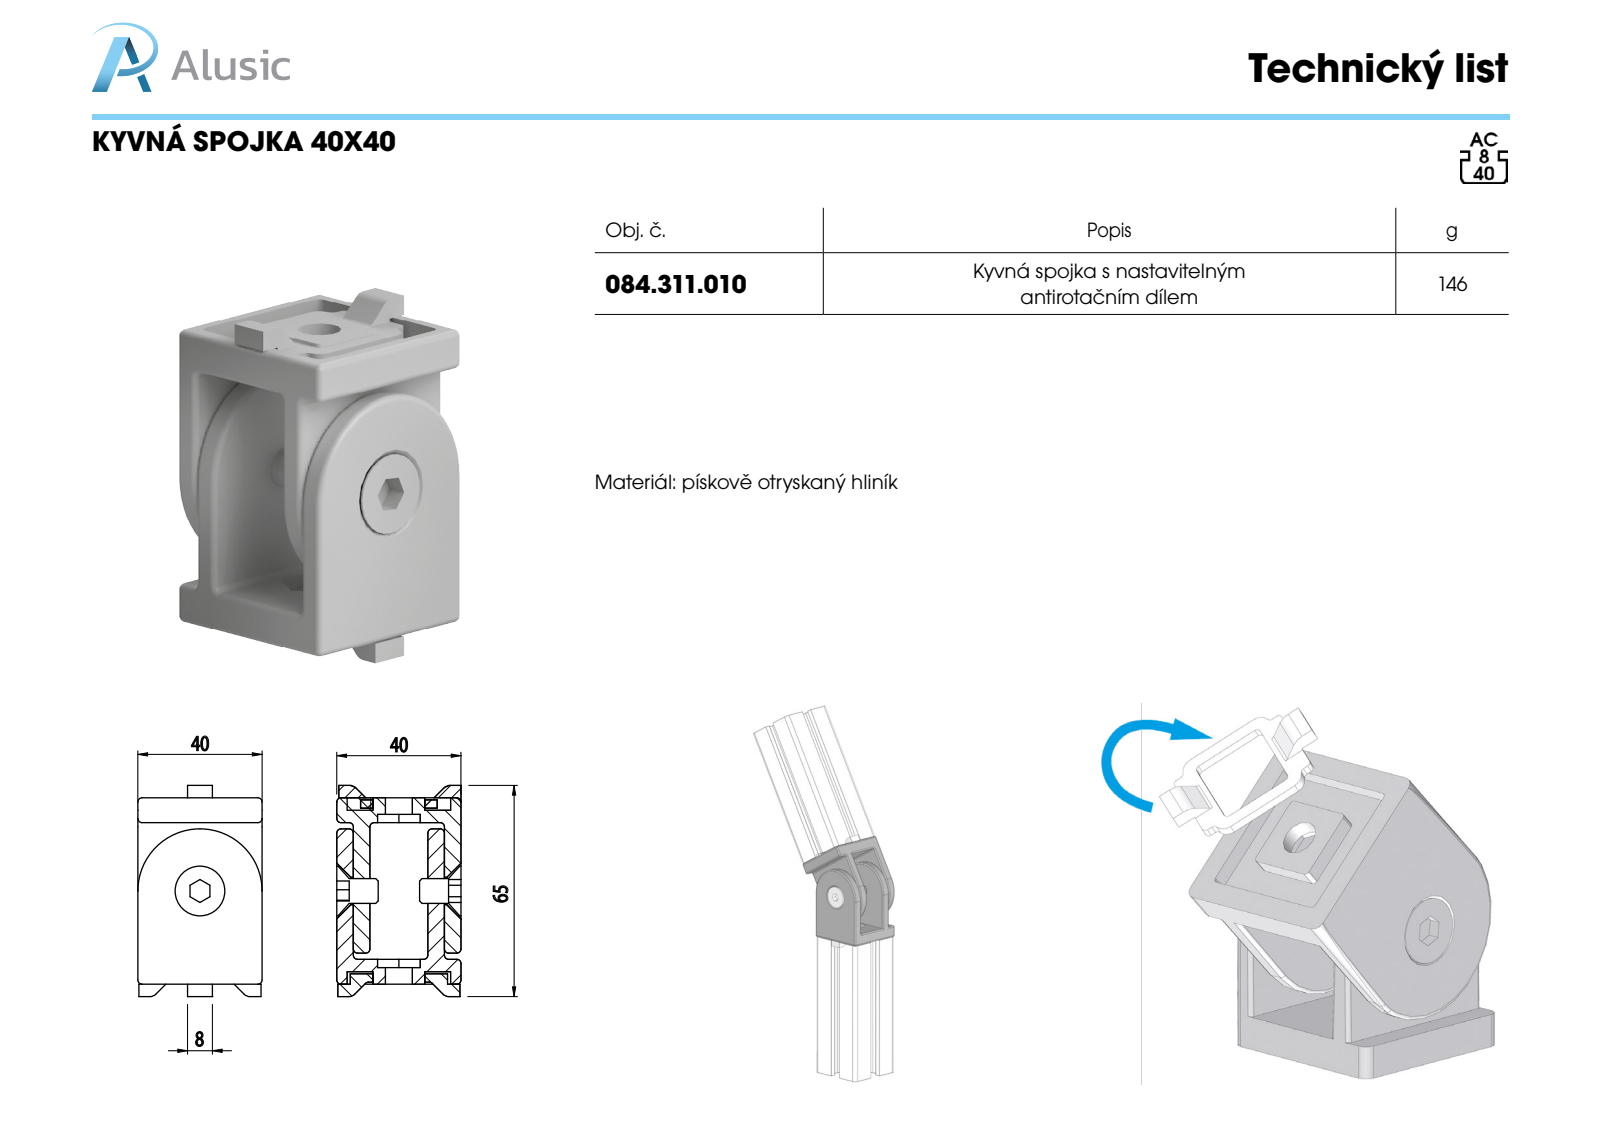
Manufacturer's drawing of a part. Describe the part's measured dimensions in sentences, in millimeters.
The part is named "084.311.010; 084.311.010-2; 084.311.010-1". Its 3-D file was written by "SolidWorks 2011 (CONFIG_CONTROL_DESIGN)". It is 4 solids with 264 faces: 106 planar, 118 cylindrical and 40 other. Overall it measures 73 by 40 by 40 millimeters. Its volume is 57 420 cubic millimeters and its surface area 27 890 square millimeters. Round holes: 2 of diameter 9, 1 of diameter 6.8. Round bosses or shafts: 1 of diameter 40. Partial cylindrical surfaces (rounded edges, fillets, slot ends): 54 of radius 1, 4 of radius 3, 4 of radius 4. The main face-to-face distances are 6, 28, 4, 34, 12, 22, 40, 8, 57, 16.
